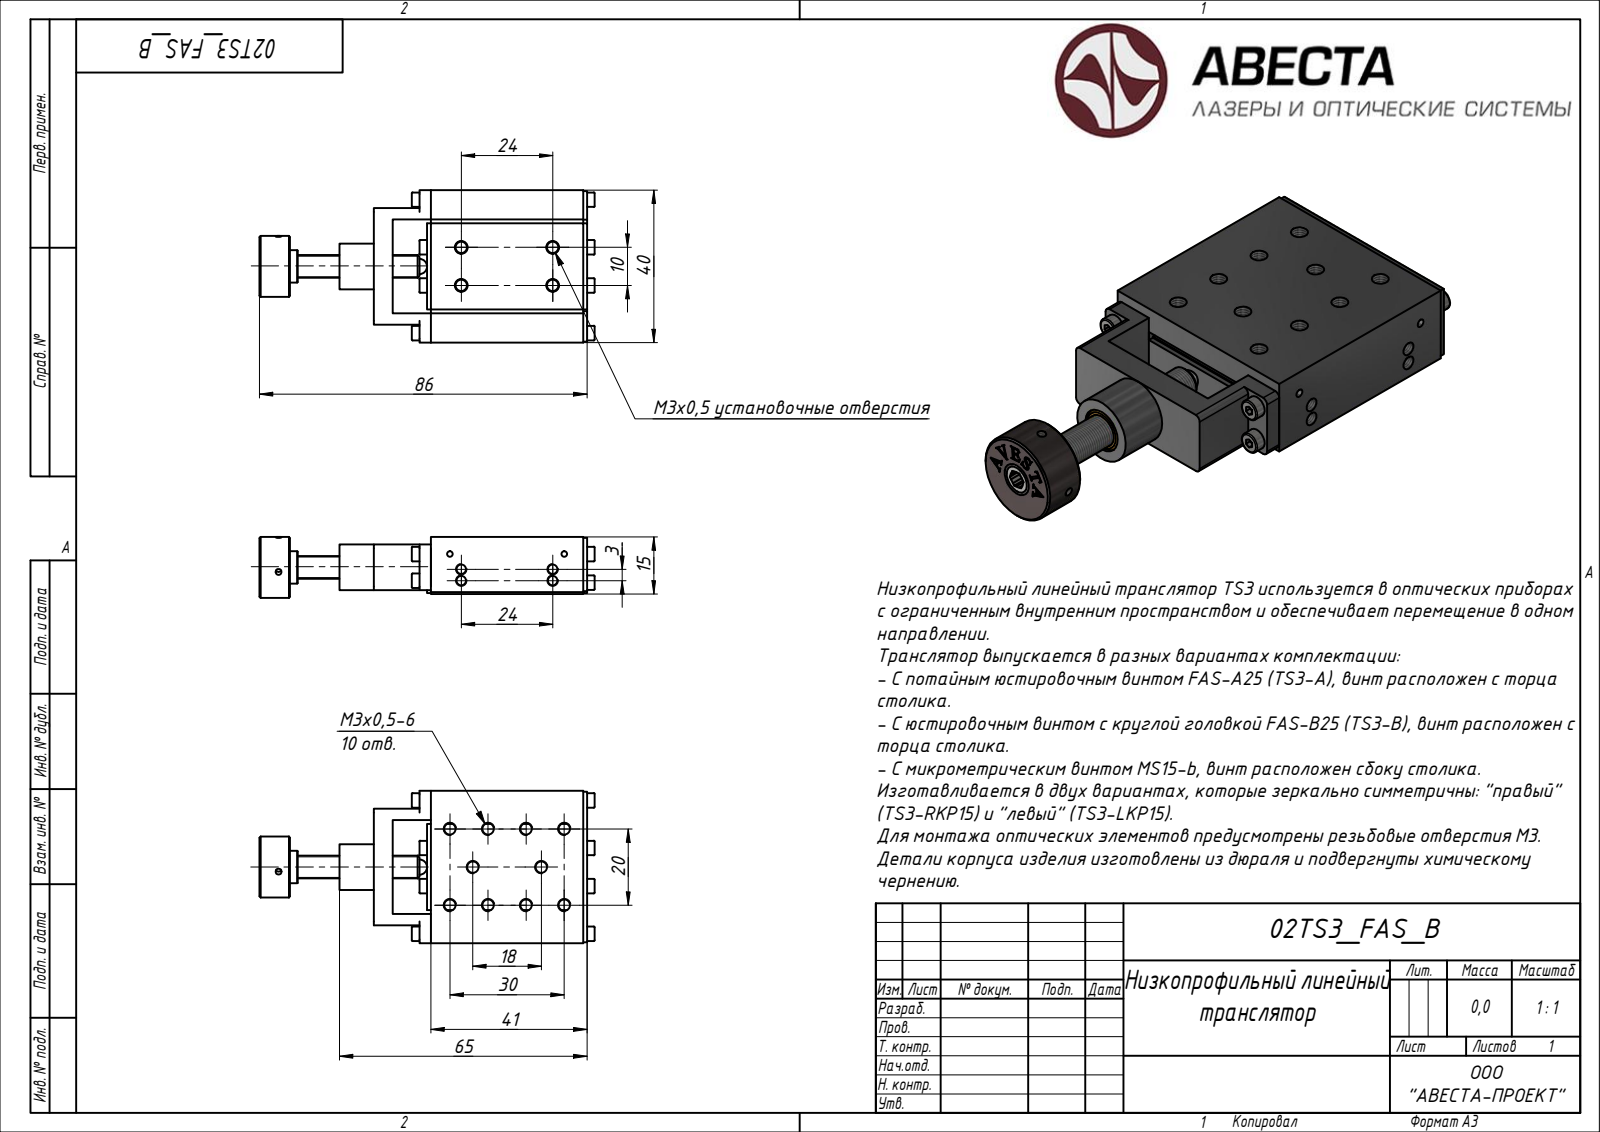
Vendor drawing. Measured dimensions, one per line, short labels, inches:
name: 02_TS3_FAS_Shell
written by: Autodesk Inventor 2019 (AUTOMOTIVE_DESIGN)
unit: in
bodies: 1 solid, 528 faces (320 planar, 96 cylindrical, 112 other)
size: 3.465 × 1.575 × 0.63
volume: 1.568 in³; area: 27.31 in²
holes: 16× ⌀0.118, 6× ⌀0.079, 4× ⌀0.059, 4× ⌀0.098, 2× ⌀0.062, 1× ⌀0.122, 1× ⌀0.236, 1× ⌀0.315, 1× ⌀0.394
bosses: 6× ⌀0.15, 4× ⌀0.118, 2× ⌀0.079, 1× ⌀0.63, 1× ⌀0.472, 1× ⌀0.354, 1× ⌀0.335, 1× ⌀0.236
rounds: 8× R0.039, 4× R0.079, 2× R0.043
face distances: 0.02, 0.197, 0.374, 0.079, 0.276, 0.118, 0.394, 0.354, 0.591, 0.315
hole spacings: 0.394, 0.23, 0.787, 0.88, 1.024, 0.945, 0.059, 0.118
